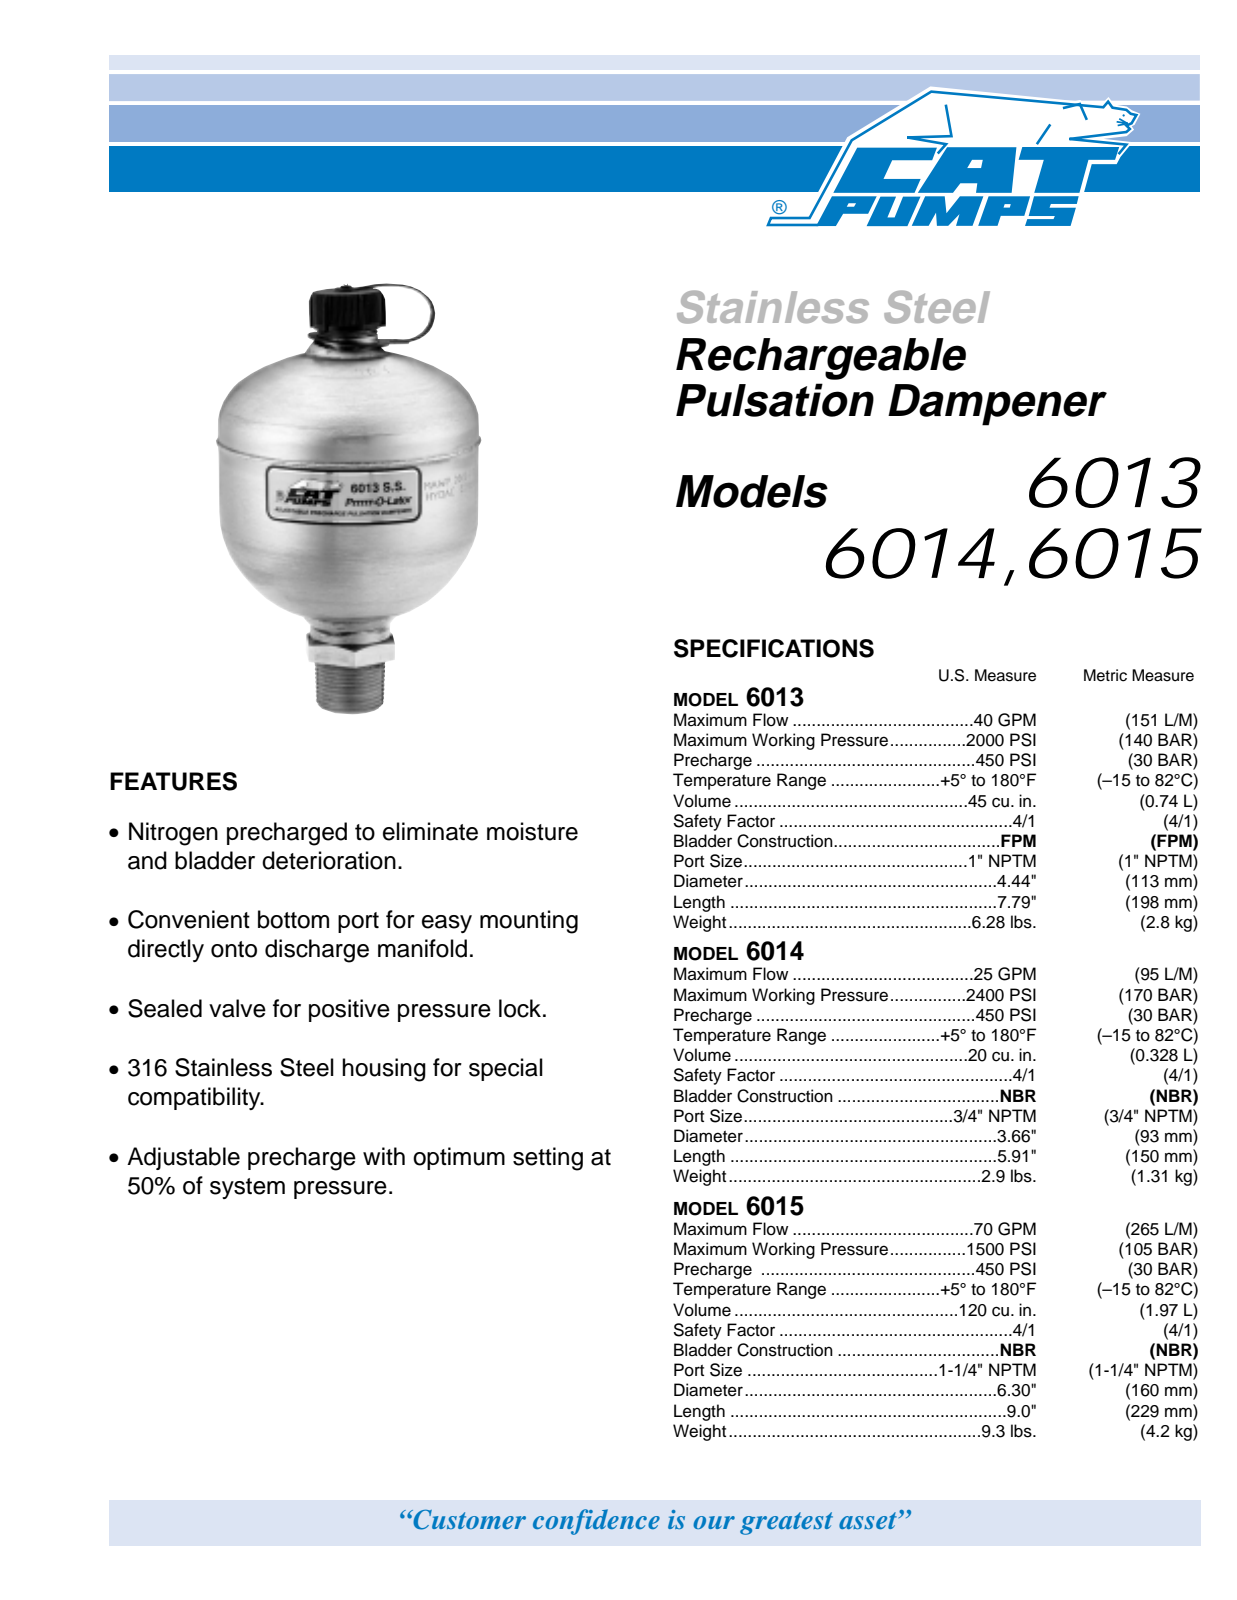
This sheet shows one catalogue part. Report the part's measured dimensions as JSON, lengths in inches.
{"part_name": "6013; 6013_body; acc_top", "step_written_by": "SolidWorks 2008 (AUTOMOTIVE_DESIGN)", "units": "inches", "bodies": {"solids": 2, "faces": 92, "planar": 22, "cylindrical": 10, "other": 60}, "overall_size": [7.837, 4.44, 4.44], "volume_in3": 66.56, "surface_area_in2": 92.28, "round_holes": [[0.602, 1]], "round_bosses_or_shafts": [[4.44, 1], [1.158, 1], [1.1, 1], [0.532, 1]], "face_to_face_distances": [7.028, 7.837, 0.809, 1.518, 5.51, 6.319, 0.985, 0.533, 6.043, 6.852]}
